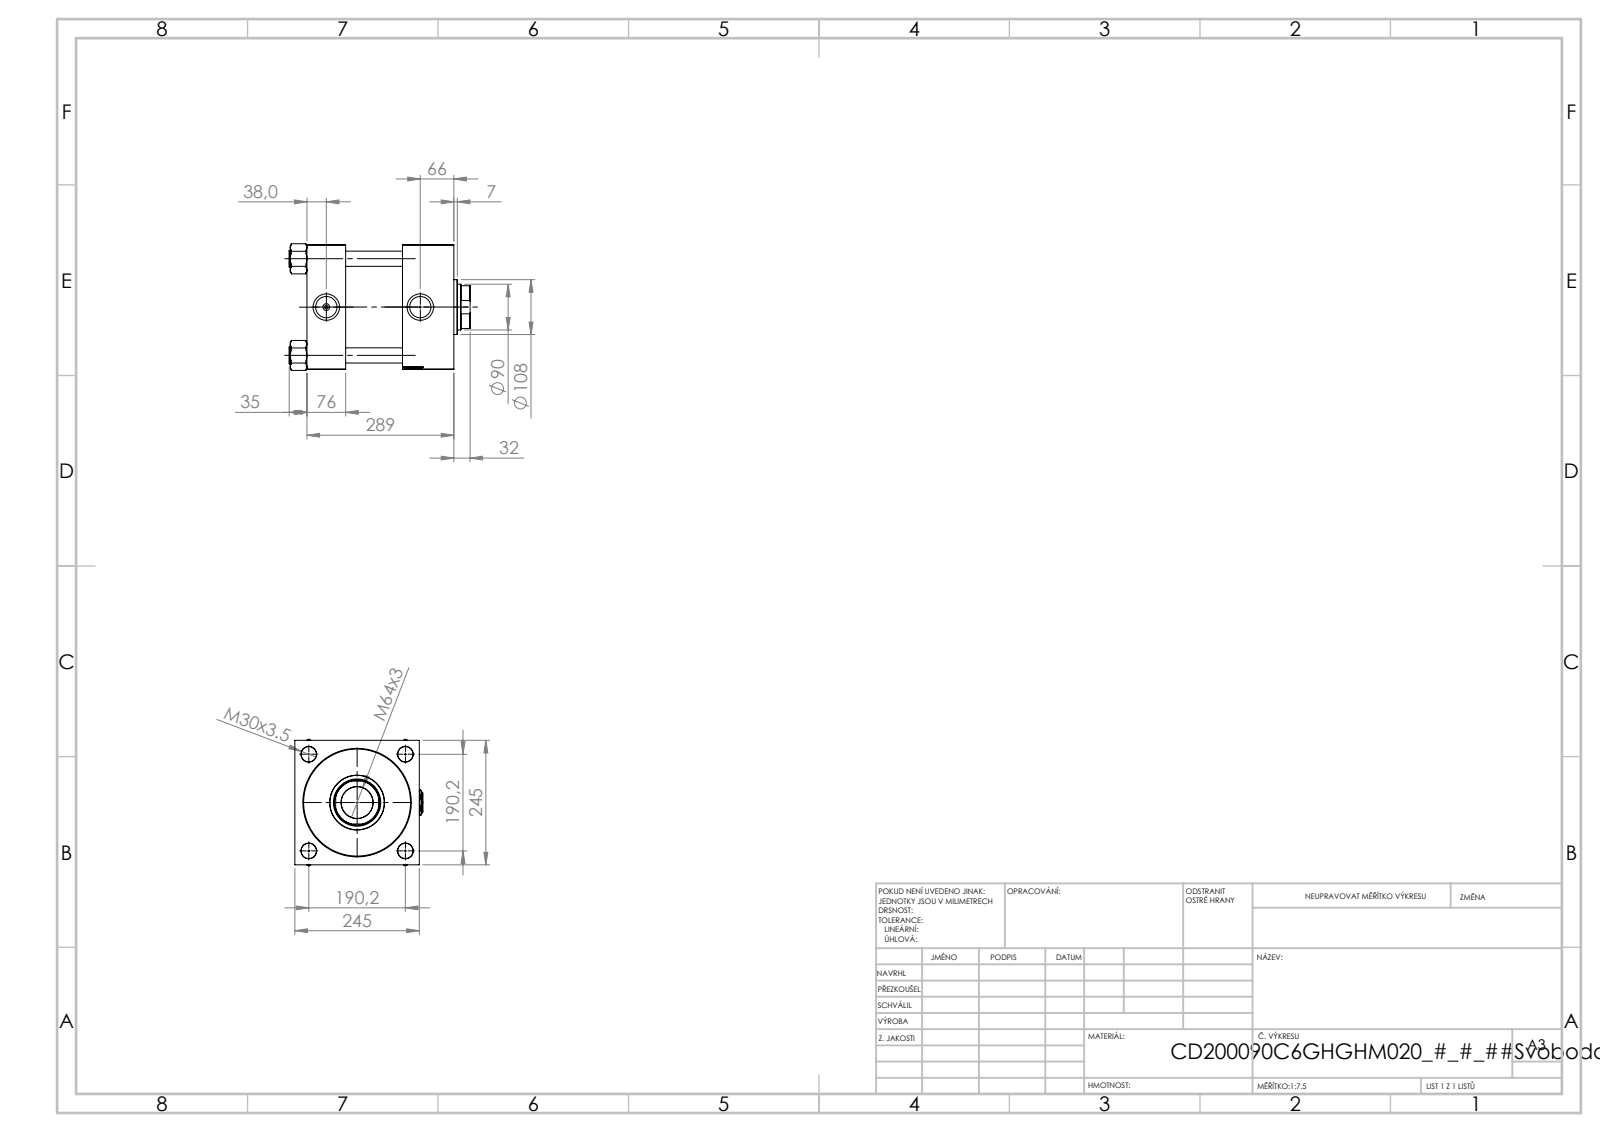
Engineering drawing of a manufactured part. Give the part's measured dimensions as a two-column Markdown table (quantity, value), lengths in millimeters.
| quantity | value |
| --- | --- |
| part name | V215CD_Body_C; V215CD_VCP_C; V215CD_C_TYCINKA; NUT_M5_V215CD_C (+2 more) |
| STEP written by | SolidWorks 2019 (CONFIG_CONTROL_DESIGN) |
| units | millimeters |
| bodies | 13 solids, 1297 faces (621 planar, 98 cylindrical, 578 other) |
| overall size | 356 × 252 × 249.44 |
| volume | 13 380 000 mm³ |
| surface area | 1 056 000 mm² |
| round holes (diameter × count) | 30 × 4, 7 × 2, 41.92 × 2, 52 × 2, 62.5 × 1, 90 × 1, 93 × 1, 146 × 1, 200 × 1, 210.5 × 1 |
| round bosses / shafts (diameter × count) | 33 × 4, 206 × 1, 108 × 1 |
| partial cylindrical surfaces (radius × count) | 44 × 1 |
| main face-to-face distances | 245, 76, 289, 213, 260.3, 184.3, 28.7, 188, 112, 72.3 |
| hole center spacings | 134.49, 190.2, 268.98, 185 |
